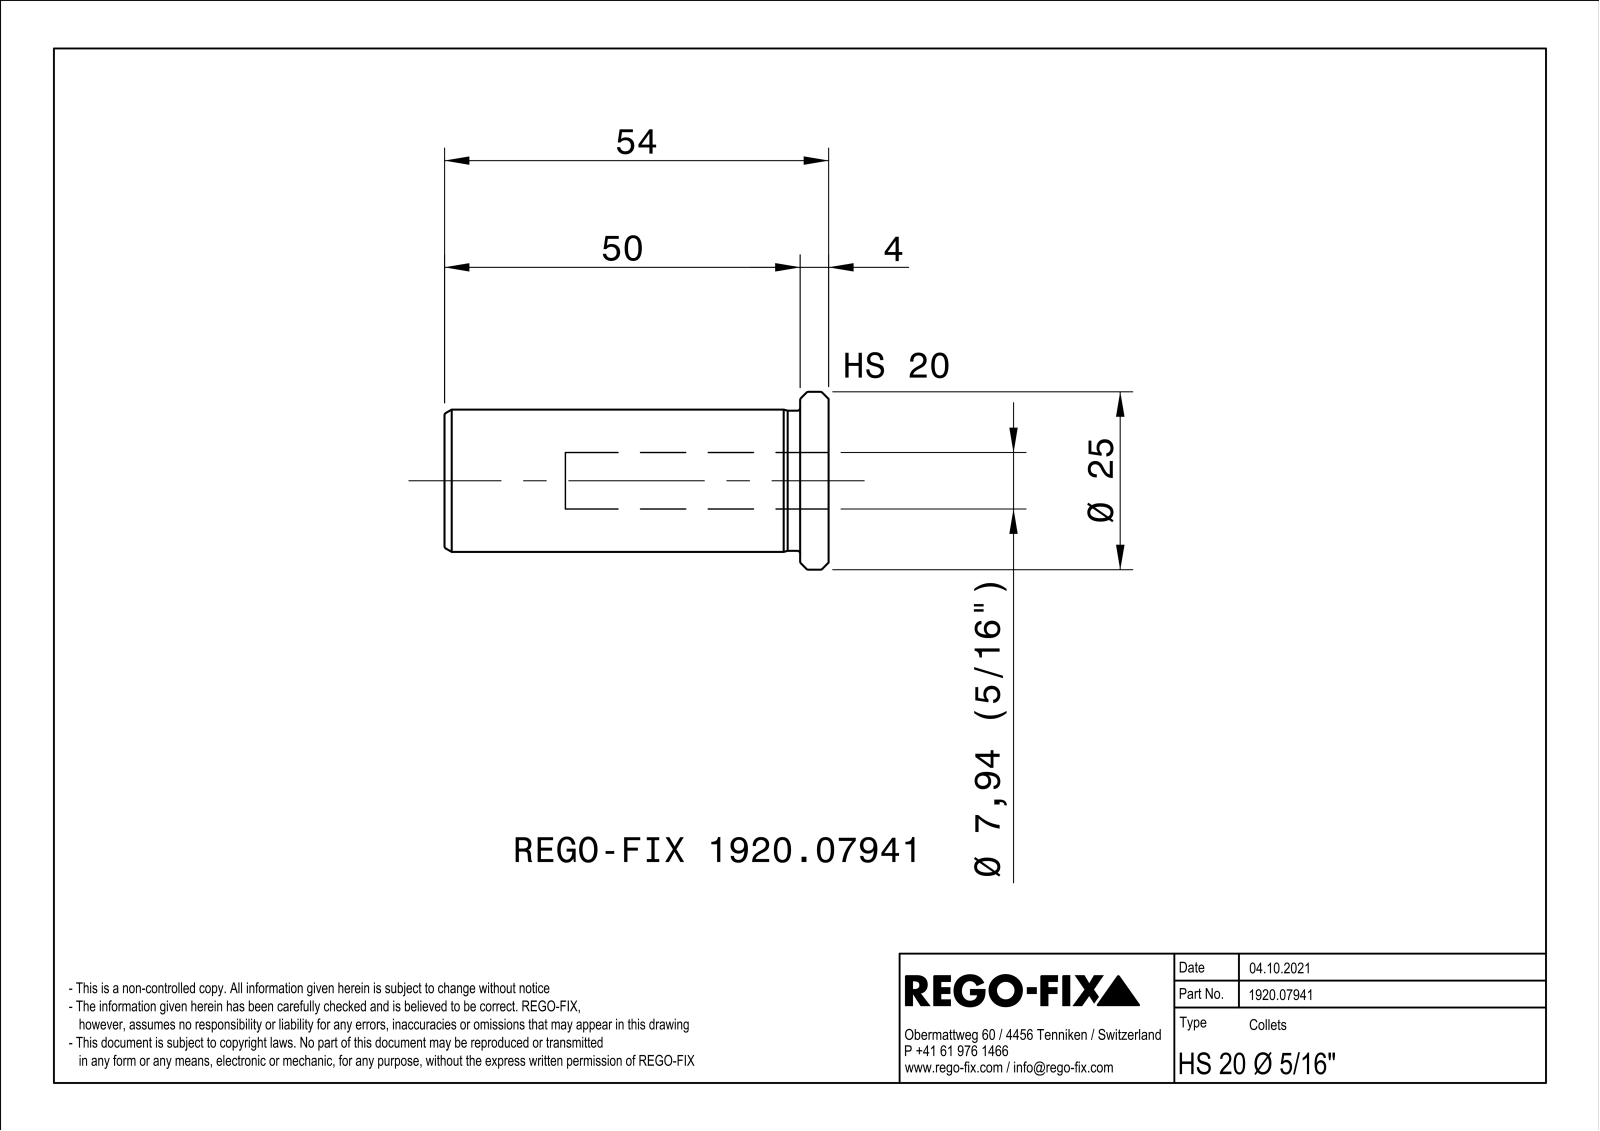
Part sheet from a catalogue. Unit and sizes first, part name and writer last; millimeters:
Units: millimetres
Overall size (bounding box): 54 × 24.98 × 24.98
Round holes (diameter × count): ⌀7.94 ×1, ⌀10.5 ×1, ⌀16.5 ×1
Round bosses / shafts (diameter × count): ⌀25 ×1, ⌀20 ×1, ⌀19.7 ×1
Main face-to-face distances: 1, 4, 54, 50
Volume: 12 112 mm³ · Surface area: 7 042 mm²
Bodies: 1 solid, 72 faces (22 planar, 12 cylindrical, 38 other)
Part name (STEP PRODUCT): NOCUT
STEP written by: SIEMENS PLM Software Solid Edge ST10 (AUTOMOTIVE_DESIGN)
